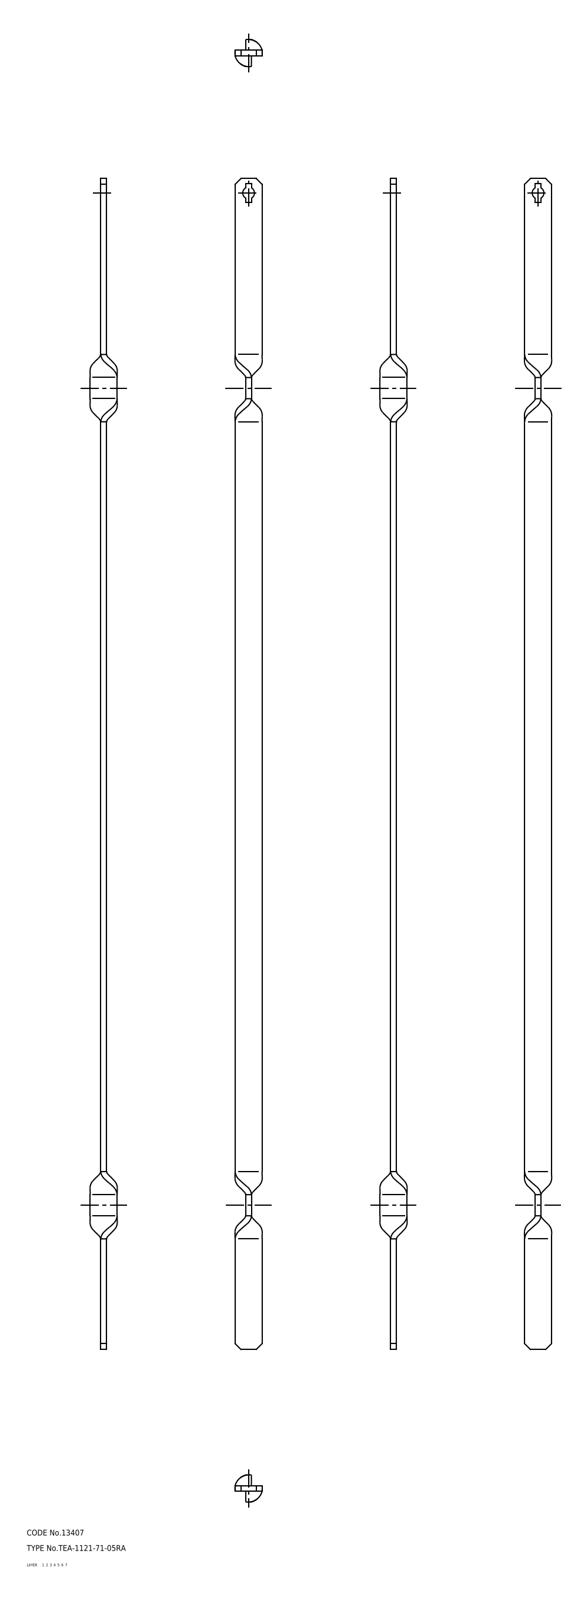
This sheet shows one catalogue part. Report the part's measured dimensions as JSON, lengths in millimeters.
{"part_name": "rod", "step_written_by": "CADfix (AUTOMOTIVE_DESIGN)", "units": "millimeters", "bodies": {"solids": 1, "faces": 34, "planar": 0, "cylindrical": 0, "other": 34}, "overall_size": [609, 14.2, 14.18], "volume_mm3": 25393, "surface_area_mm2": 20910}
